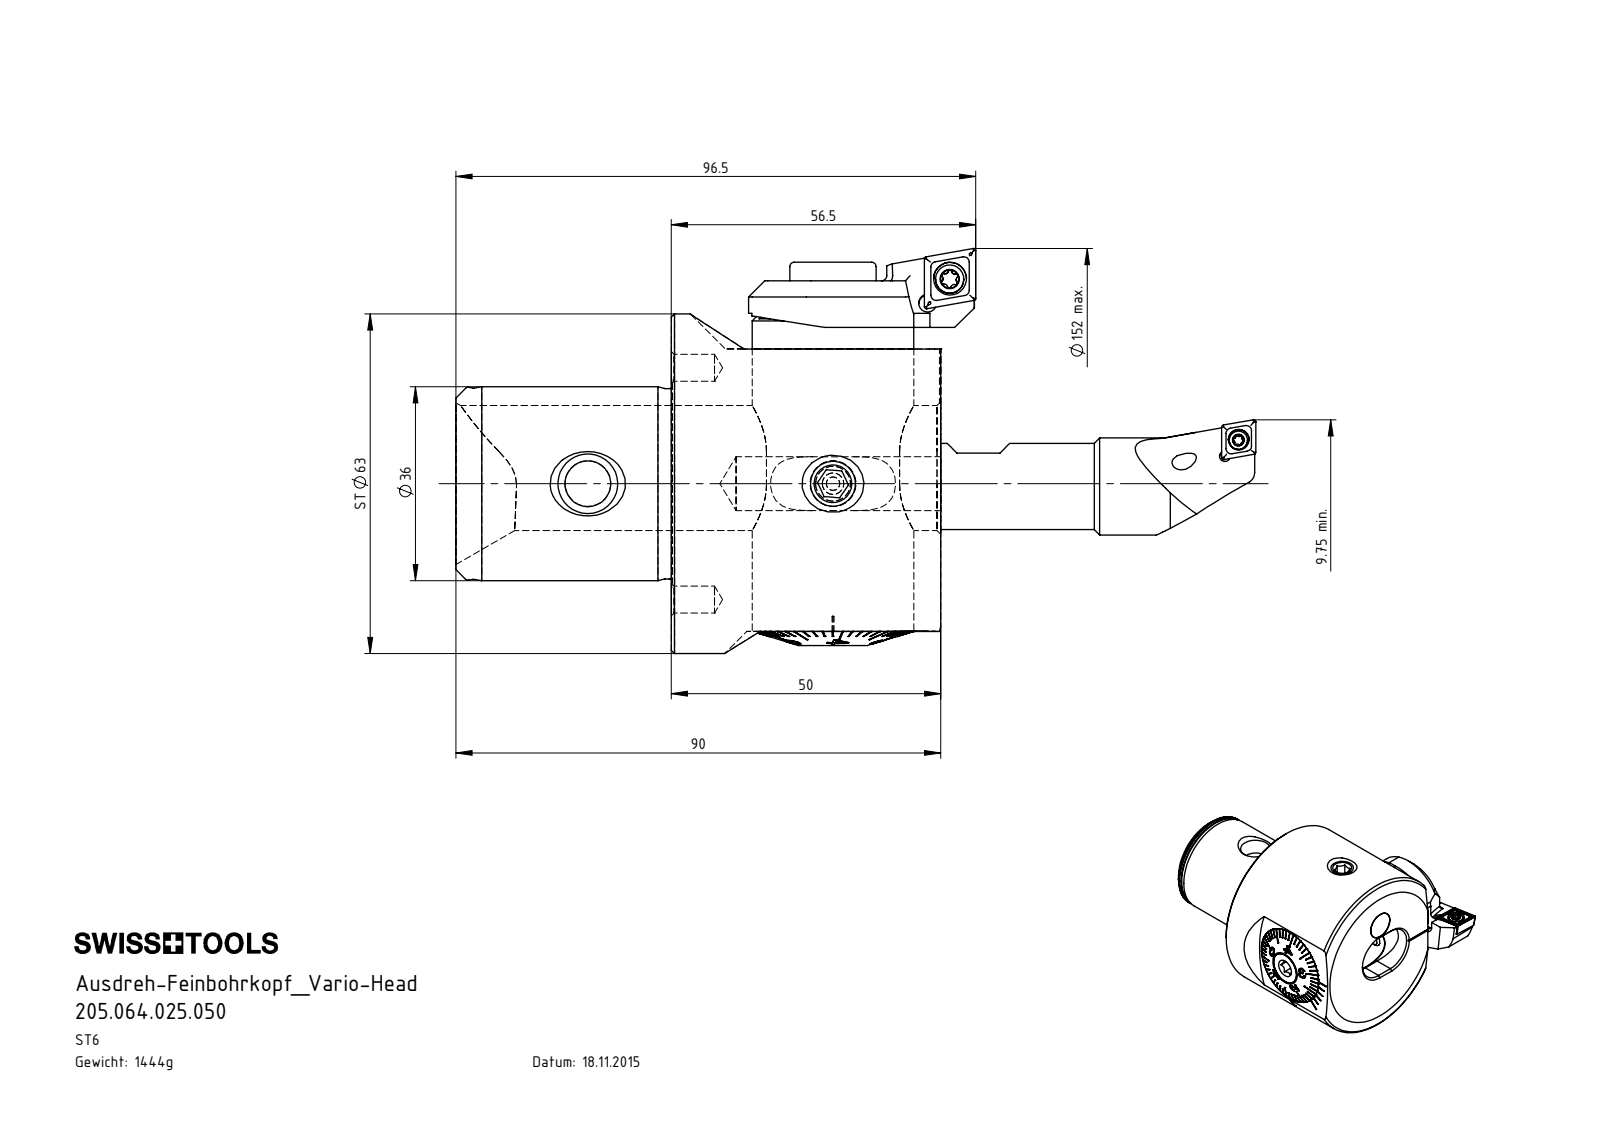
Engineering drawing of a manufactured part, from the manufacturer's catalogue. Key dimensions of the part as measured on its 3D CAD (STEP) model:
Part name (STEP PRODUCT): DIN 7984 - M3 x 8_DIN 7984 - M3 x 5; ST6-ER2.001.012_A; ISO 4026 - M10 x 18; A55-BG2.012.006_B (+8 more)
STEP written by: SolidWorks 2022 (CONFIG_CONTROL_DESIGN)
Units: millimetres
Bodies: 16 solids, 814 faces (341 planar, 147 cylindrical, 326 other)
Overall size (bounding box): 90 × 65.31 × 64
Volume: 153 597 mm³ · Surface area: 47 277 mm²
Round holes (diameter × count): ⌀8.5 ×3, ⌀3.3 ×2, ⌀5 ×2, ⌀6 ×2, ⌀1 ×1, ⌀2.5 ×1, ⌀4.2 ×1, ⌀8 ×1, ⌀10 ×1, ⌀11.75 ×1, ⌀12 ×1, ⌀12.4 ×1
Round bosses / shafts (diameter × count): ⌀10 ×2, ⌀64 ×1, ⌀63 ×1, ⌀36 ×1, ⌀35.8 ×1, ⌀35.3 ×1, ⌀30 ×1, ⌀29.98 ×1
Partial cylindrical surfaces — rounded edges, fillets, slot ends (radius × count): R0.5 ×8, R1.4 ×4, R1.9 ×4, R3.2 ×3, R1.5 ×2, R5.47 ×2, R8.5 ×2, R18.05 ×2
Main face-to-face distances: 50, 57.7, 2.5, 5.3, 45.49, 53, 7.51, 50.5, 5.01, 6.5
Hole centre spacings: 25.93, 10.5, 14.39, 14.6, 16.64, 19.79, 23.21, 27.25
